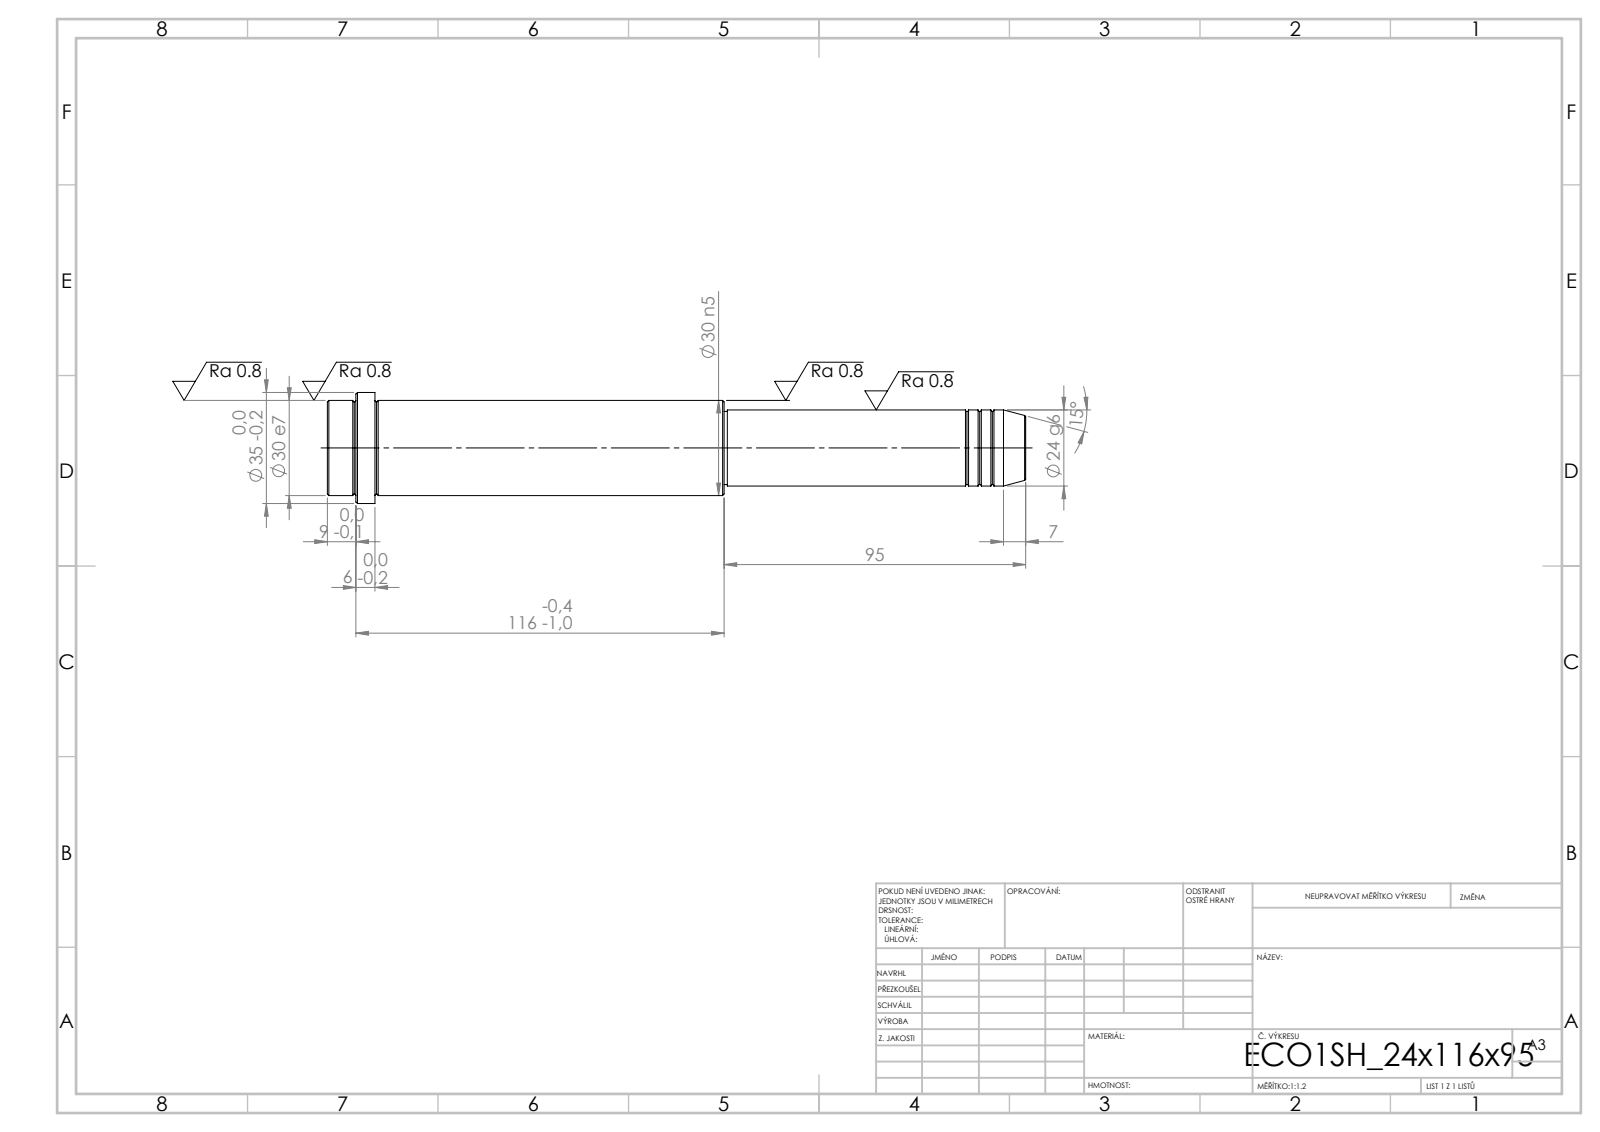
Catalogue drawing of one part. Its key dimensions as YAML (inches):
step_written_by: "SolidWorks 2019 (CONFIG_CONTROL_DESIGN)"
units: inches
bodies: {solids: 1, faces: 52, planar: 6, cylindrical: 16, other: 30}
overall_size: [8.661, 1.378, 1.378]
volume: 8.065
surface_area: 32.56
round_bosses_or_shafts:
  - {diameter: 1.378, count: 1}
  - {diameter: 1.181, count: 1}
  - {diameter: 0.945, count: 1}
  - {diameter: 0.906, count: 1}
face_to_face_distances: [8.661, 8.071, 0.591, 3.74, 4.331, 4.921, 8.307, 4.567, 0.236, 0.354]
